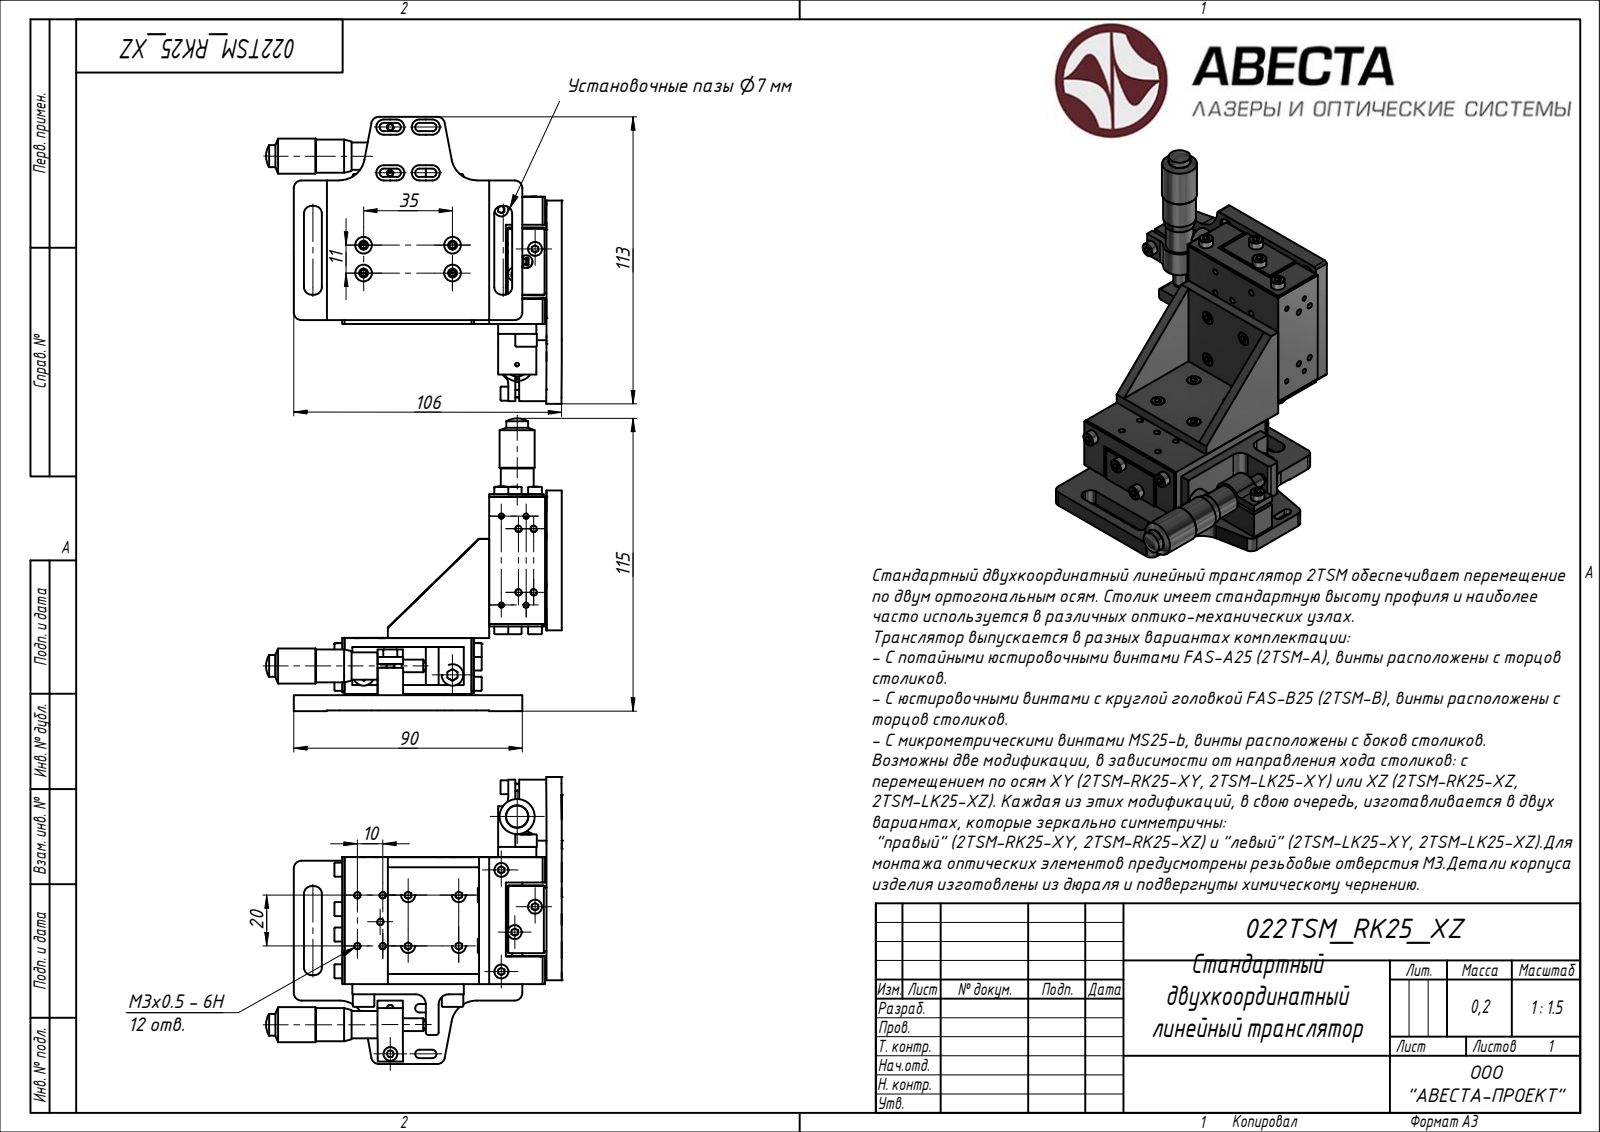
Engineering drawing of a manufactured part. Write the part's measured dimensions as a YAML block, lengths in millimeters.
part_name: "Block 03; Block 02; Block 01"
step_written_by: "ST-DEVELOPER v15 (AUTOMOTIVE_DESIGN)"
units: millimeters
bodies: {solids: 38, faces: 1521, planar: 0, cylindrical: 0, other: 1521}
overall_size: [116.43, 115.27, 112.97]
